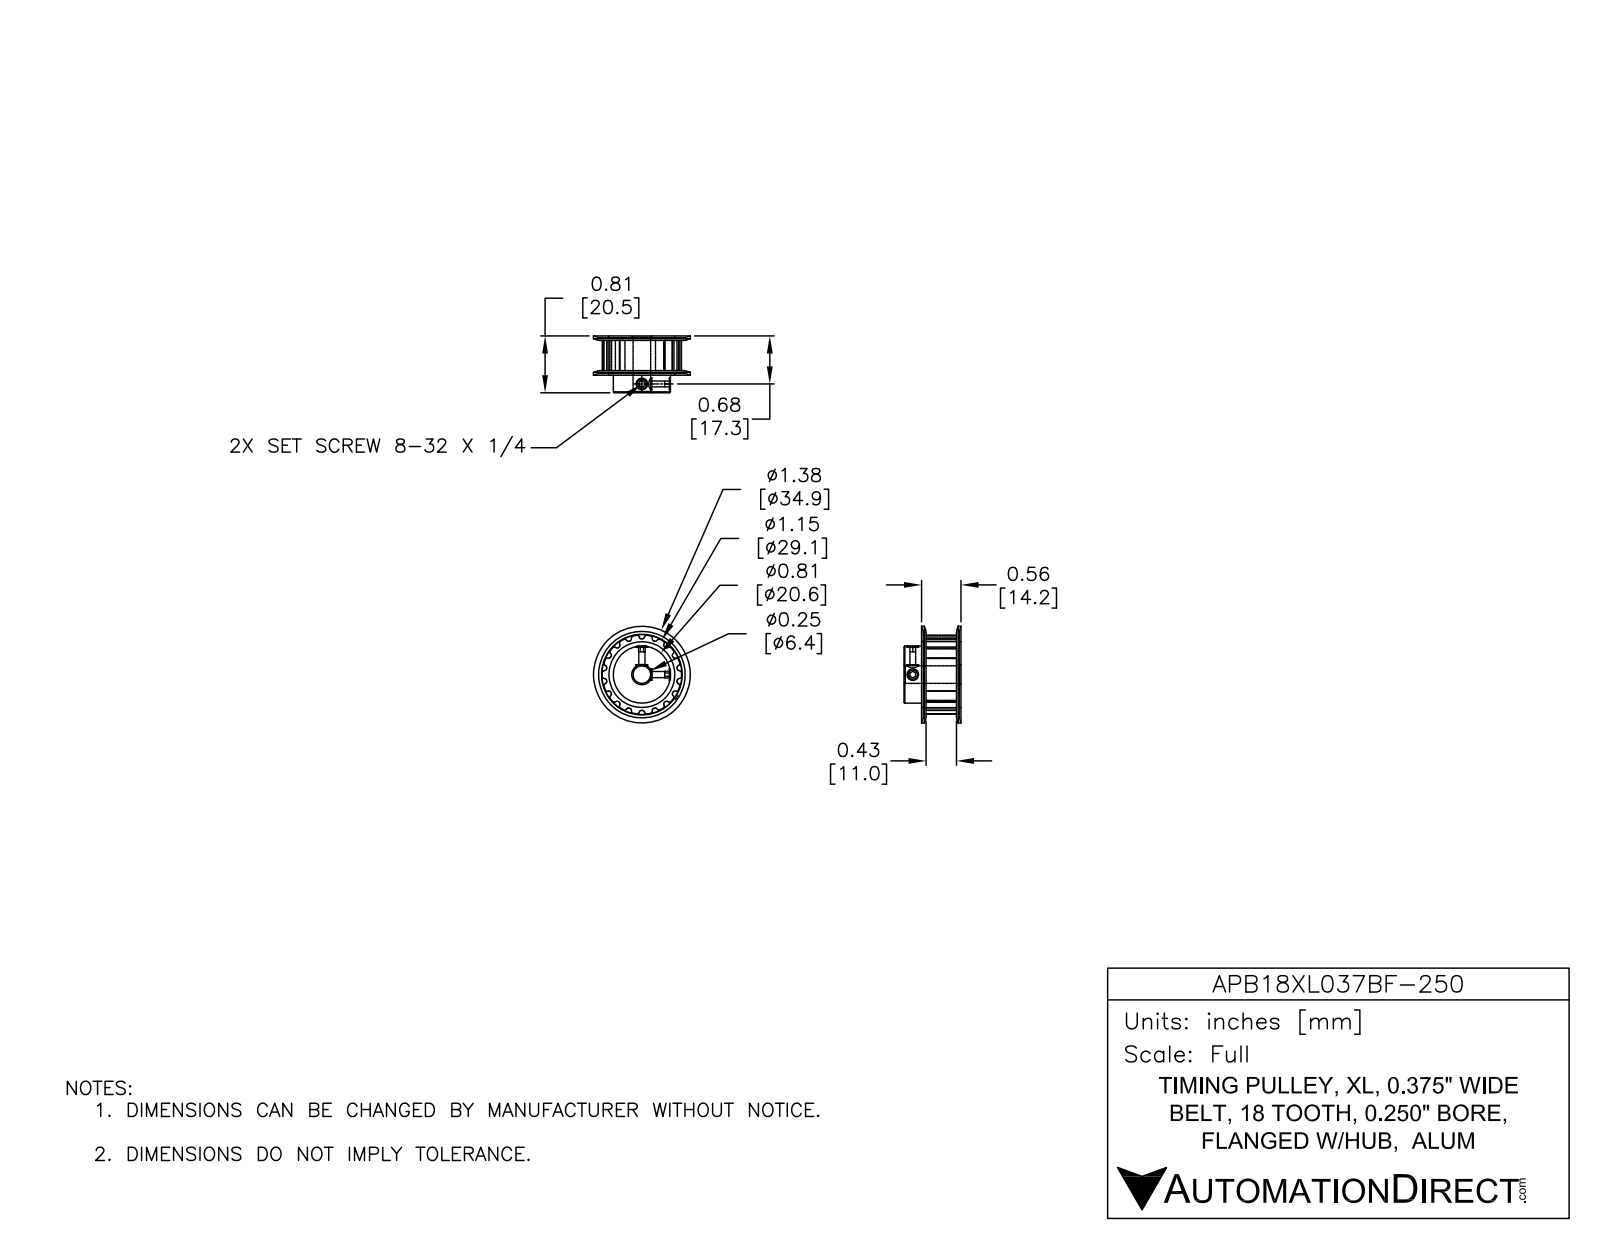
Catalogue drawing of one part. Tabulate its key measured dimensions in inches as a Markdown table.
| quantity | value |
| --- | --- |
| part name | APB18XL037BF-250 |
| STEP written by | SolidWorks 2014 (AUTOMOTIVE_DESIGN) |
| units | inches |
| bodies | 1 solid, 197 faces (60 planar, 115 cylindrical, 22 other) |
| overall size | 1.375 × 1.375 × 0.813 |
| volume | 0.614 in³ |
| surface area | 7.788 in² |
| round holes (diameter × count) | 0.088 × 2, 0.25 × 1 |
| round bosses / shafts (diameter × count) | 0.813 × 1 |
| partial cylindrical surfaces (radius × count) | 0.015 × 72, 0.508 × 1 |
| main face-to-face distances | 0.495, 0.033, 0.528, 0.813, 0.78, 0.285, 1.126, 0.383, 0.383, 0.462 |
